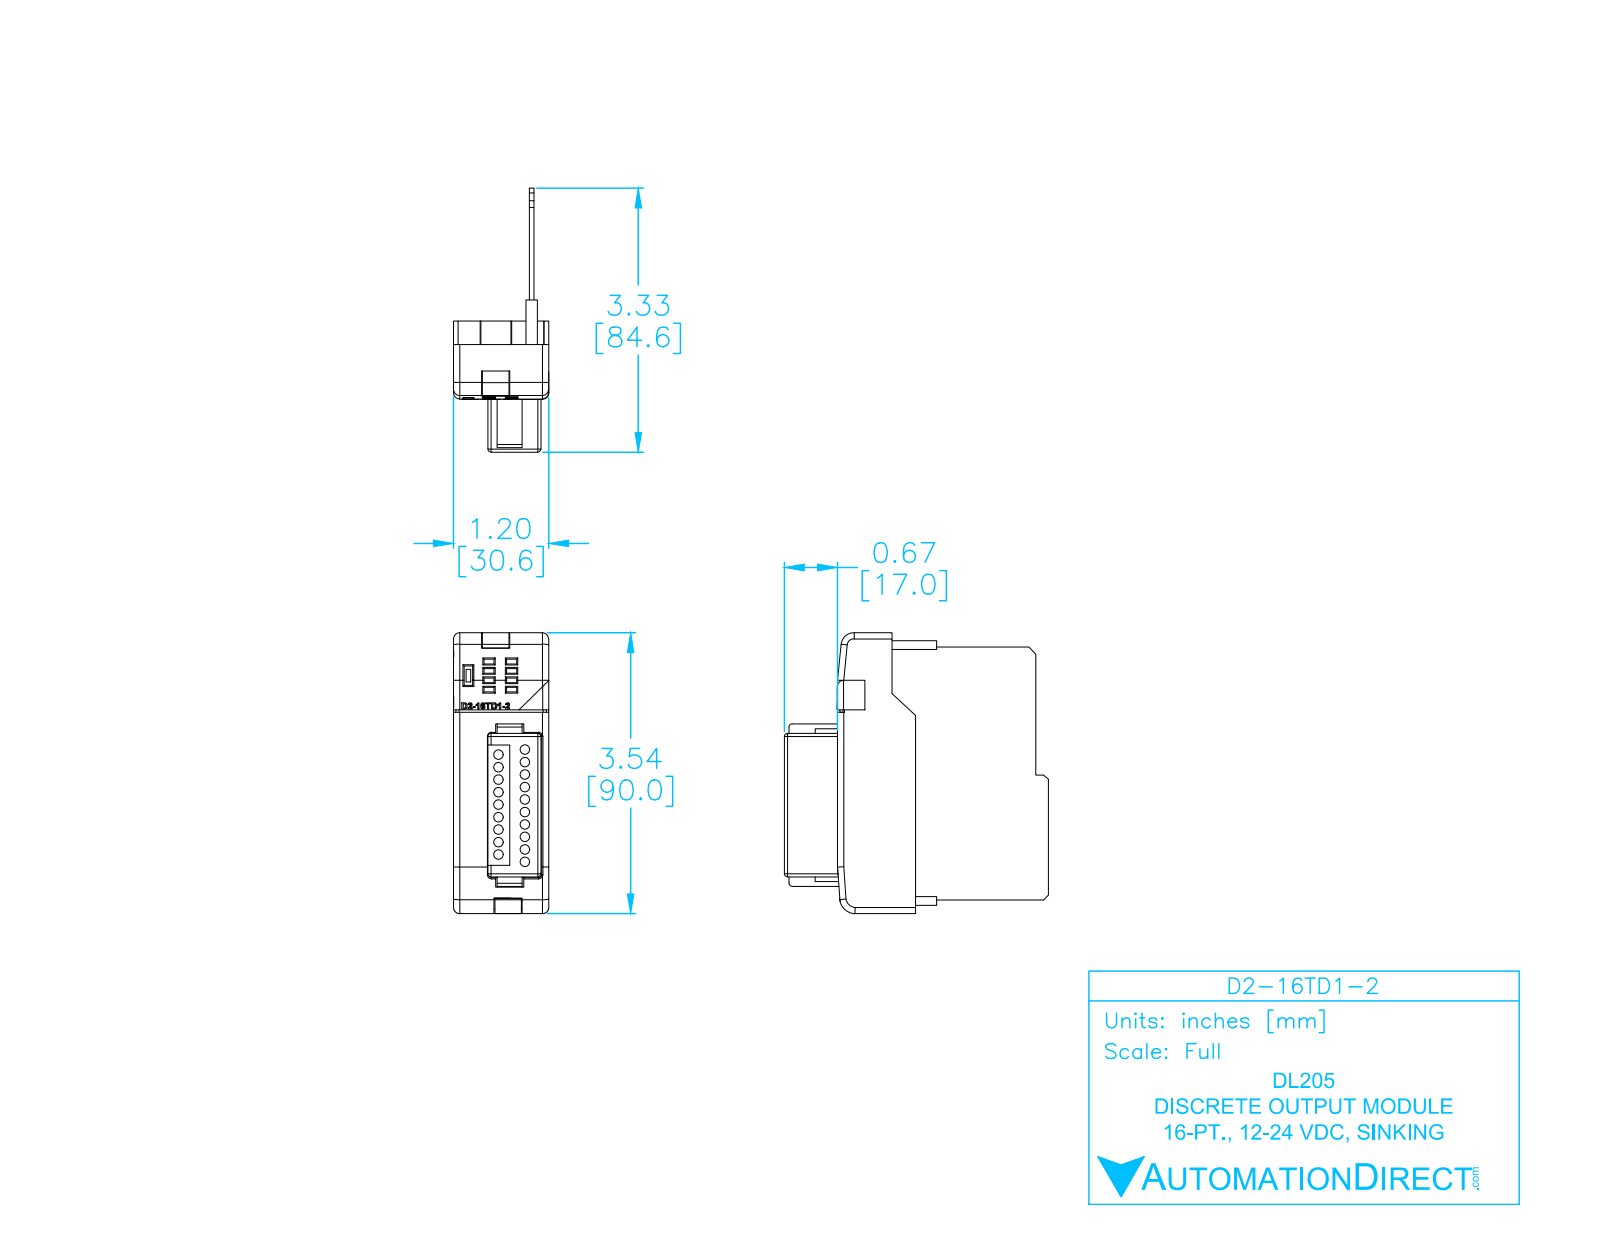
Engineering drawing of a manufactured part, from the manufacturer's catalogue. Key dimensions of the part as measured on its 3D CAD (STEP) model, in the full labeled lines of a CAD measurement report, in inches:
Part name (STEP PRODUCT): D2-16TD1-2_ModuleCase Light_NEW
STEP written by: SolidWorks 2009 (AUTOMOTIVE_DESIGN)
Units: inches
Bodies: 2 solids, 643 faces (412 planar, 158 cylindrical, 73 other)
Overall size (bounding box): 3.543 × 3.331 × 1.203
Volume: 1.865 in³ · Surface area: 50.54 in²
Round holes (diameter × count): ⌀0.118 ×19
Partial cylindrical surfaces — rounded edges, fillets, slot ends (radius × count): R0.014 ×28, R0.039 ×18, R0.02 ×12, R0.079 ×11, R0.01 ×6, R0.103 ×1, R0.149 ×1, R0.162 ×1
Main face-to-face distances: 0.059, 0.186, 0.127, 0.245, 0.02, 0.039, 0.956, 1.142, 0.709, 0.433
Hole centre spacings: 0.157, 0.315, 0.472, 0.63, 0.339, 0.345, 0.787, 0.4
